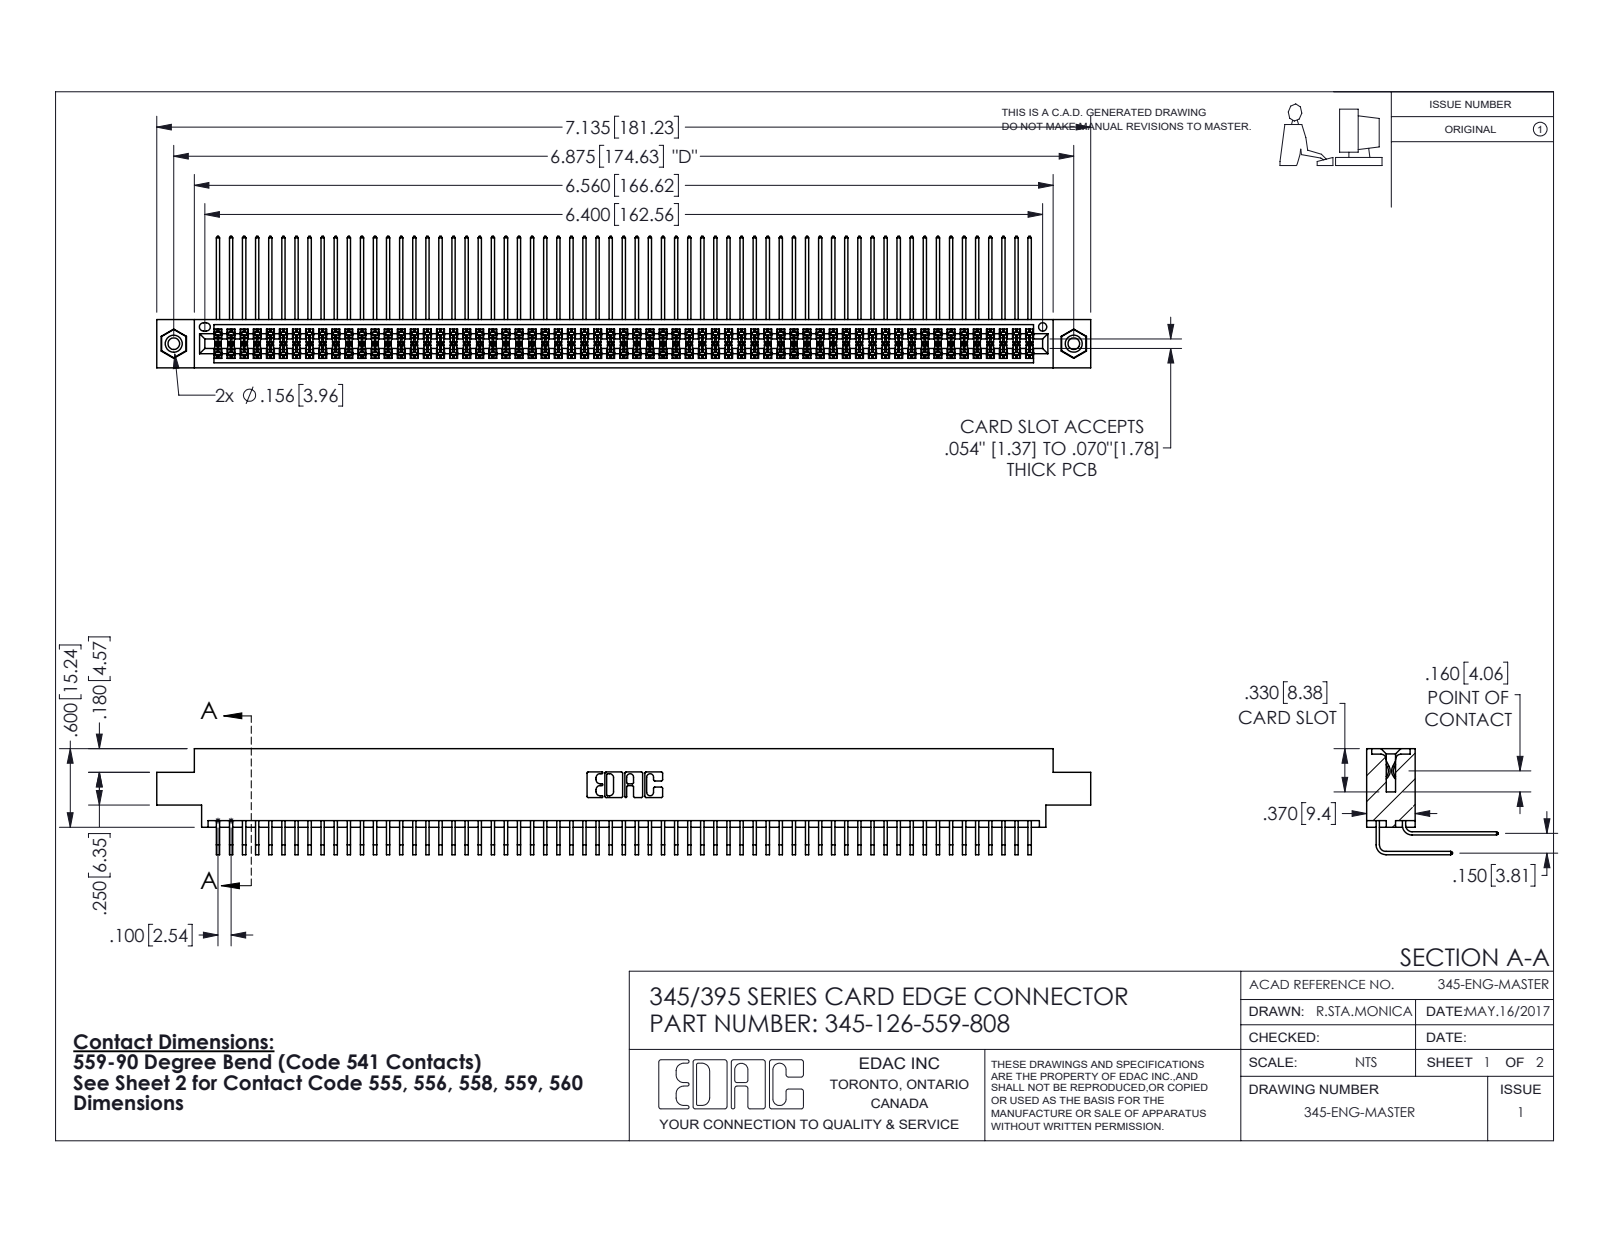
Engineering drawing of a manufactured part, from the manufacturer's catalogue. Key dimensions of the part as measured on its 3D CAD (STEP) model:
Part name (STEP PRODUCT): 345 Part_0.170 Offset - 0.156 Dia-TI; 345-250-001_345-250-003-102; 345-292-001_558 559 Tail - 1; 345-126-559-808 (+1 more)
STEP written by: SolidWorks 2016 (CONFIG_CONTROL_DESIGN)
Units: inches
Bodies: 129 solids, 6742 faces (4526 planar, 2200 cylindrical, 16 other)
Overall size (bounding box): 7.135 × 1.005 × 0.809
Volume: 1.123 in³ · Surface area: 48.34 in²
Round holes (diameter × count): ⌀0.089 ×2, ⌀0.125 ×2, ⌀0.156 ×2, ⌀0.064 ×1
Round bosses / shafts (diameter × count): ⌀0.155 ×2
Partial cylindrical surfaces — rounded edges, fillets, slot ends (radius × count): R0.006 ×251, R0.01 ×22, R0.007 ×6, R0.031 ×6, R0.026 ×3, R0.014 ×2, R0.019 ×2, R0.022 ×2
Main face-to-face distances: 0.072, 0.298, 0.2, 0.37, 0.098, 0.272, 0.025, 0.225, 0.175, 0.15
Hole centre spacings: 0.27, 6.639, 6.875
